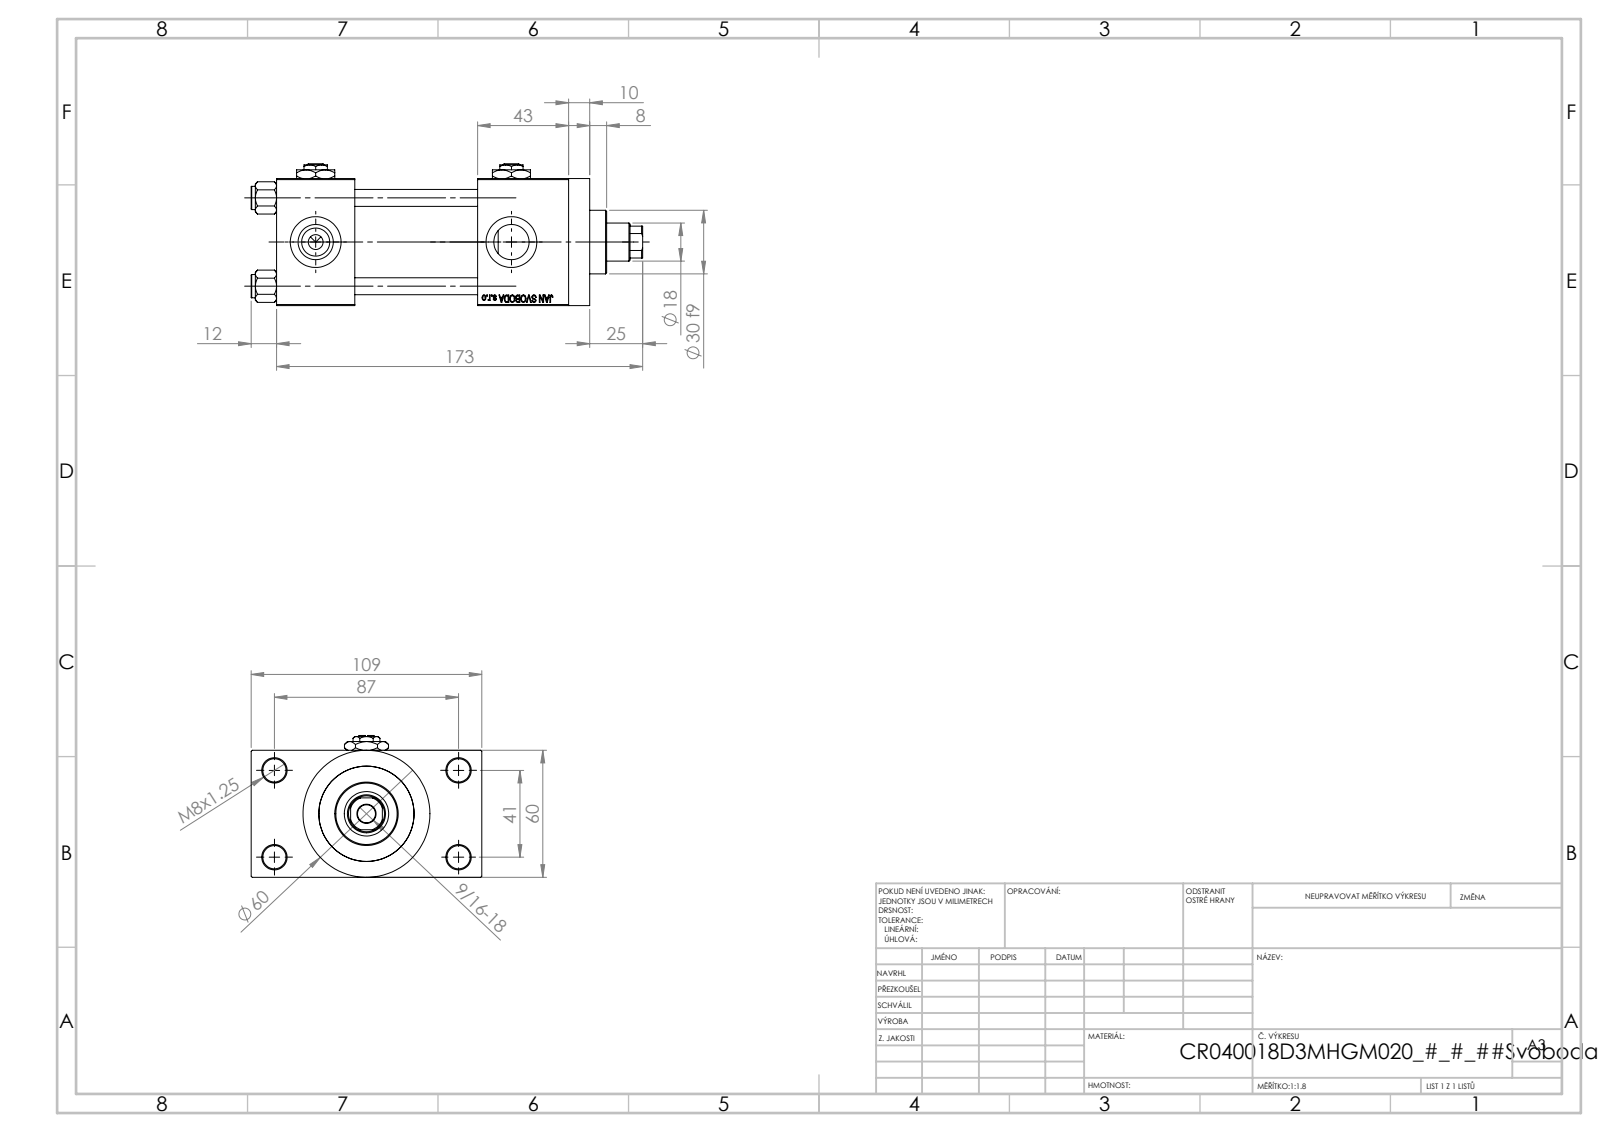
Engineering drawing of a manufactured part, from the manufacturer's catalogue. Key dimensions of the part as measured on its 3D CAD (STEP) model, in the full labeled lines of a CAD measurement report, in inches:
Part name (STEP PRODUCT): V215CR_VCP_D; V215CR_D_Body; V215_VC_A; Zatka_pro_OIL_PORT (+2 more)
STEP written by: SolidWorks 2019 (CONFIG_CONTROL_DESIGN)
Units: inches
Bodies: 13 solids, 1205 faces (546 planar, 99 cylindrical, 560 other)
Overall size (bounding box): 7.283 × 4.291 × 2.638
Volume: 31.14 in³ · Surface area: 194 in²
Round holes (diameter × count): ⌀0.315 ×4, ⌀0.433 ×4, ⌀0.656 ×4, ⌀0.945 ×4, ⌀0.276 ×3, ⌀0.335 ×1, ⌀0.709 ×1, ⌀0.827 ×1, ⌀1.22 ×1, ⌀1.575 ×1, ⌀1.772 ×1
Round bosses / shafts (diameter × count): ⌀0.433 ×4, ⌀2.362 ×1, ⌀1.811 ×1, ⌀1.181 ×1
Partial cylindrical surfaces — rounded edges, fillets, slot ends (radius × count): R0.335 ×1
Main face-to-face distances: 2.362, 2.283, 0.965, 3.327, 1.457, 3.74, 1.693, 5.433, 3.976, 0.394
Hole centre spacings: 0.892, 1.161, 1.642, 1.856, 1.893, 2.533, 3.011, 1.614
